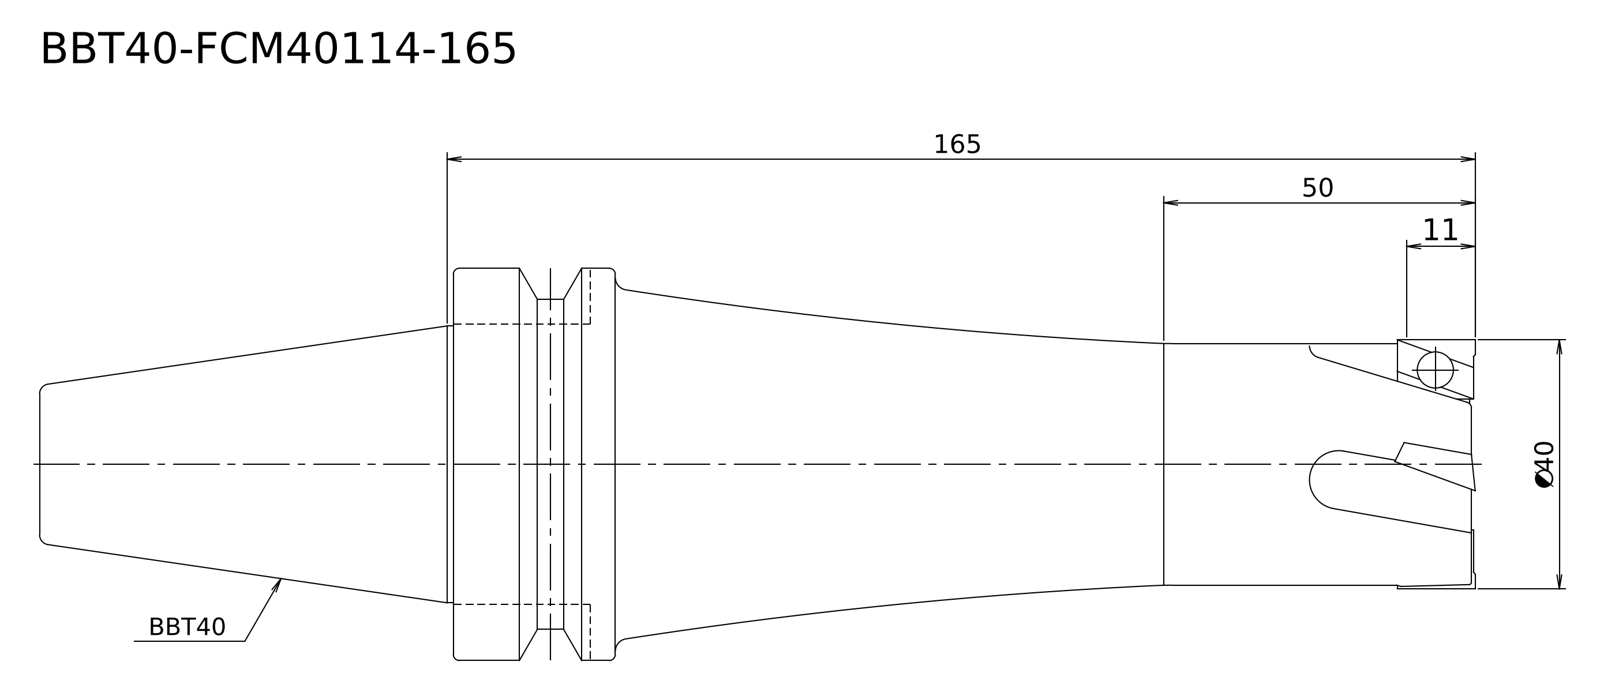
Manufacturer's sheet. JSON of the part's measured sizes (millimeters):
{"step_written_by": "Kubotek KeyCreator V8.5.1 (14335) (CONFIG_CONTROL_DESIGN)", "units": "millimeters", "bodies": {"solids": 1, "faces": 16, "planar": 4, "cylindrical": 6, "other": 6}, "overall_size": [230.4, 63, 63], "volume_mm3": 359651, "surface_area_mm2": 36567, "round_bosses_or_shafts": [[63, 1], [53, 1], [44.45, 1], [40, 1], [38.8, 1]], "face_to_face_distances": [164, 230.4, 66.4, 138, 26, 92.4]}
